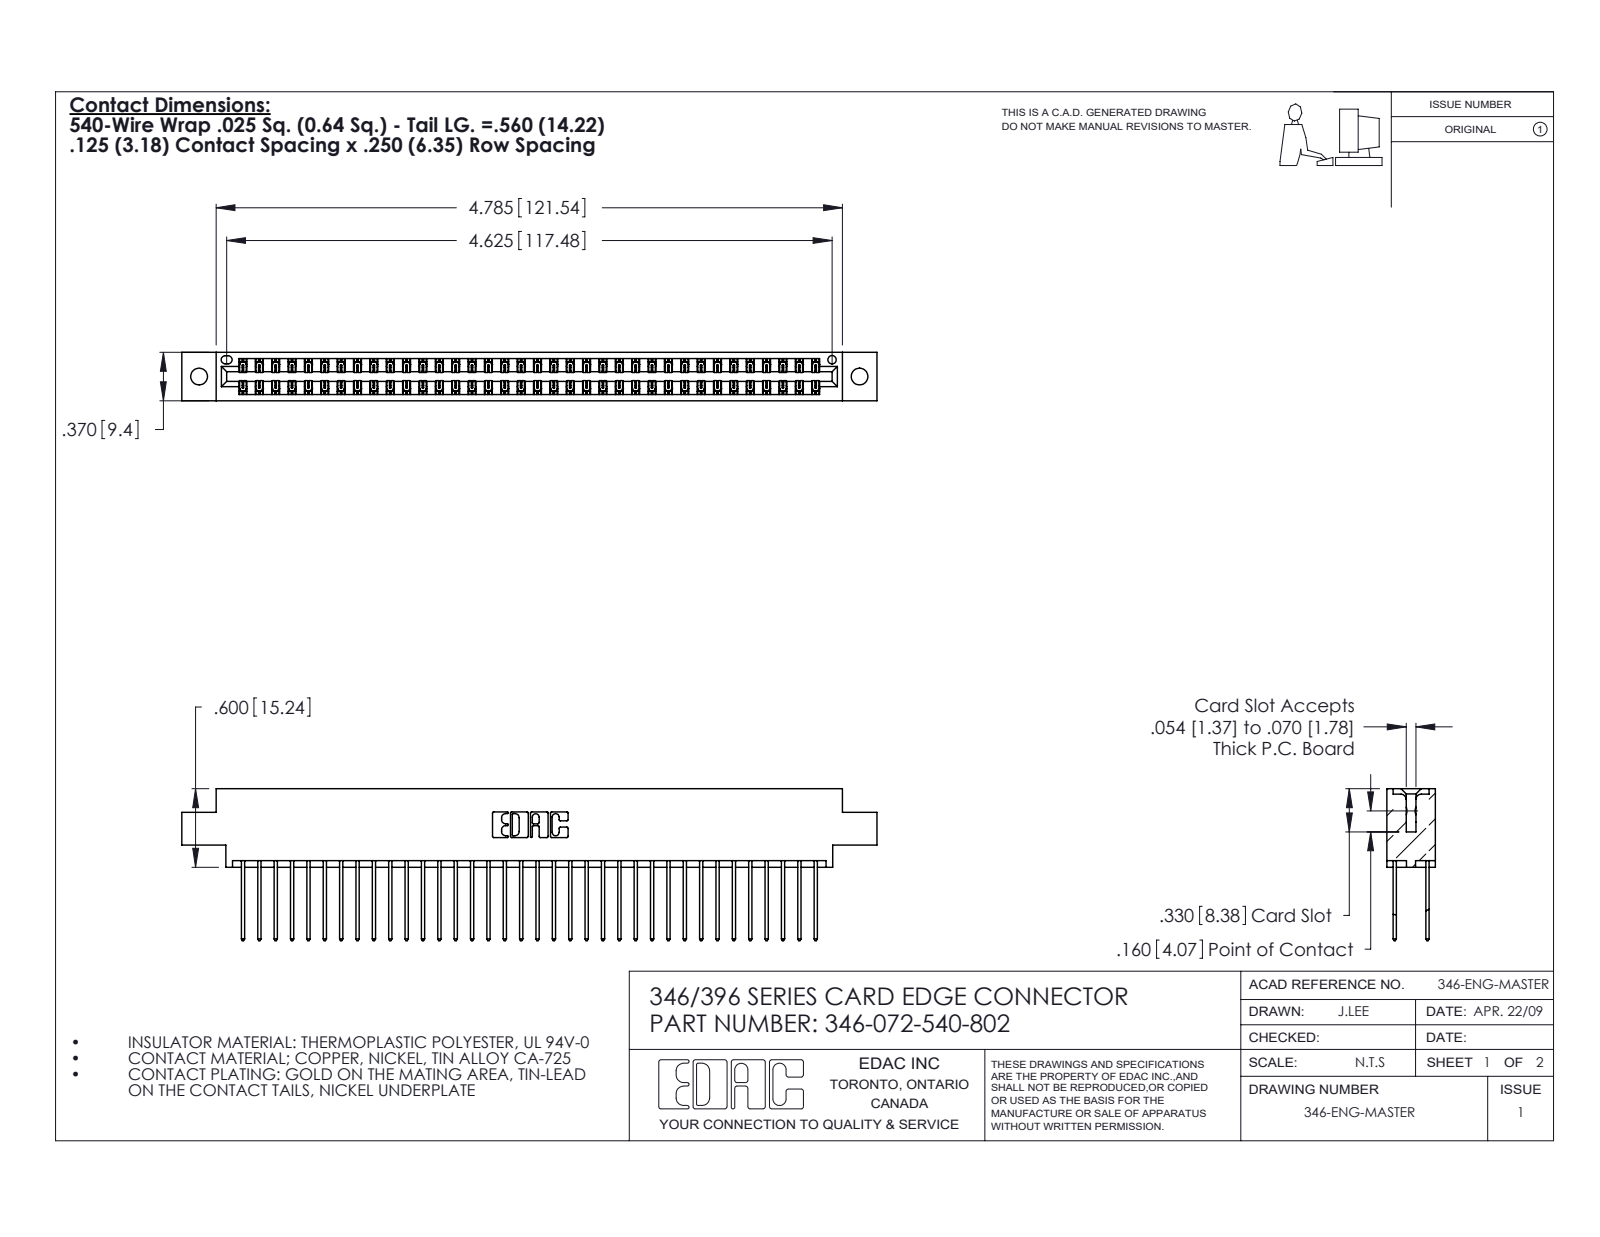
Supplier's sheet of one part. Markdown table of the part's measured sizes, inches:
| quantity | value |
| --- | --- |
| part name | 346-072-540-802; 346 Part_0.170 Offset - 0.128 Dia; 345-292-001_345-293-140 |
| STEP written by | SolidWorks 2020 (CONFIG_CONTROL_DESIGN) |
| units | inches |
| bodies | 73 solids, 3870 faces (2600 planar, 1270 cylindrical, 0 other) |
| overall size | 5.31 × 1.16 × 0.37 |
| volume | 0.805 in³ |
| surface area | 29.81 in² |
| round holes (diameter × count) | 0.128 × 2, 0.064 × 1 |
| partial cylindrical surfaces (radius × count) | 0.006 × 108, 0.01 × 72, 0.01 × 22, 0.007 × 6, 0.031 × 6, 0.026 × 3, 0.014 × 2, 0.022 × 2 |
| main face-to-face distances | 0.048, 0.322, 0.25, 0.072, 0.298, 0.025, 0.37, 0.275, 0.148, 0.222 |
| hole center spacings | 0.246, 4.836, 5.045 |
